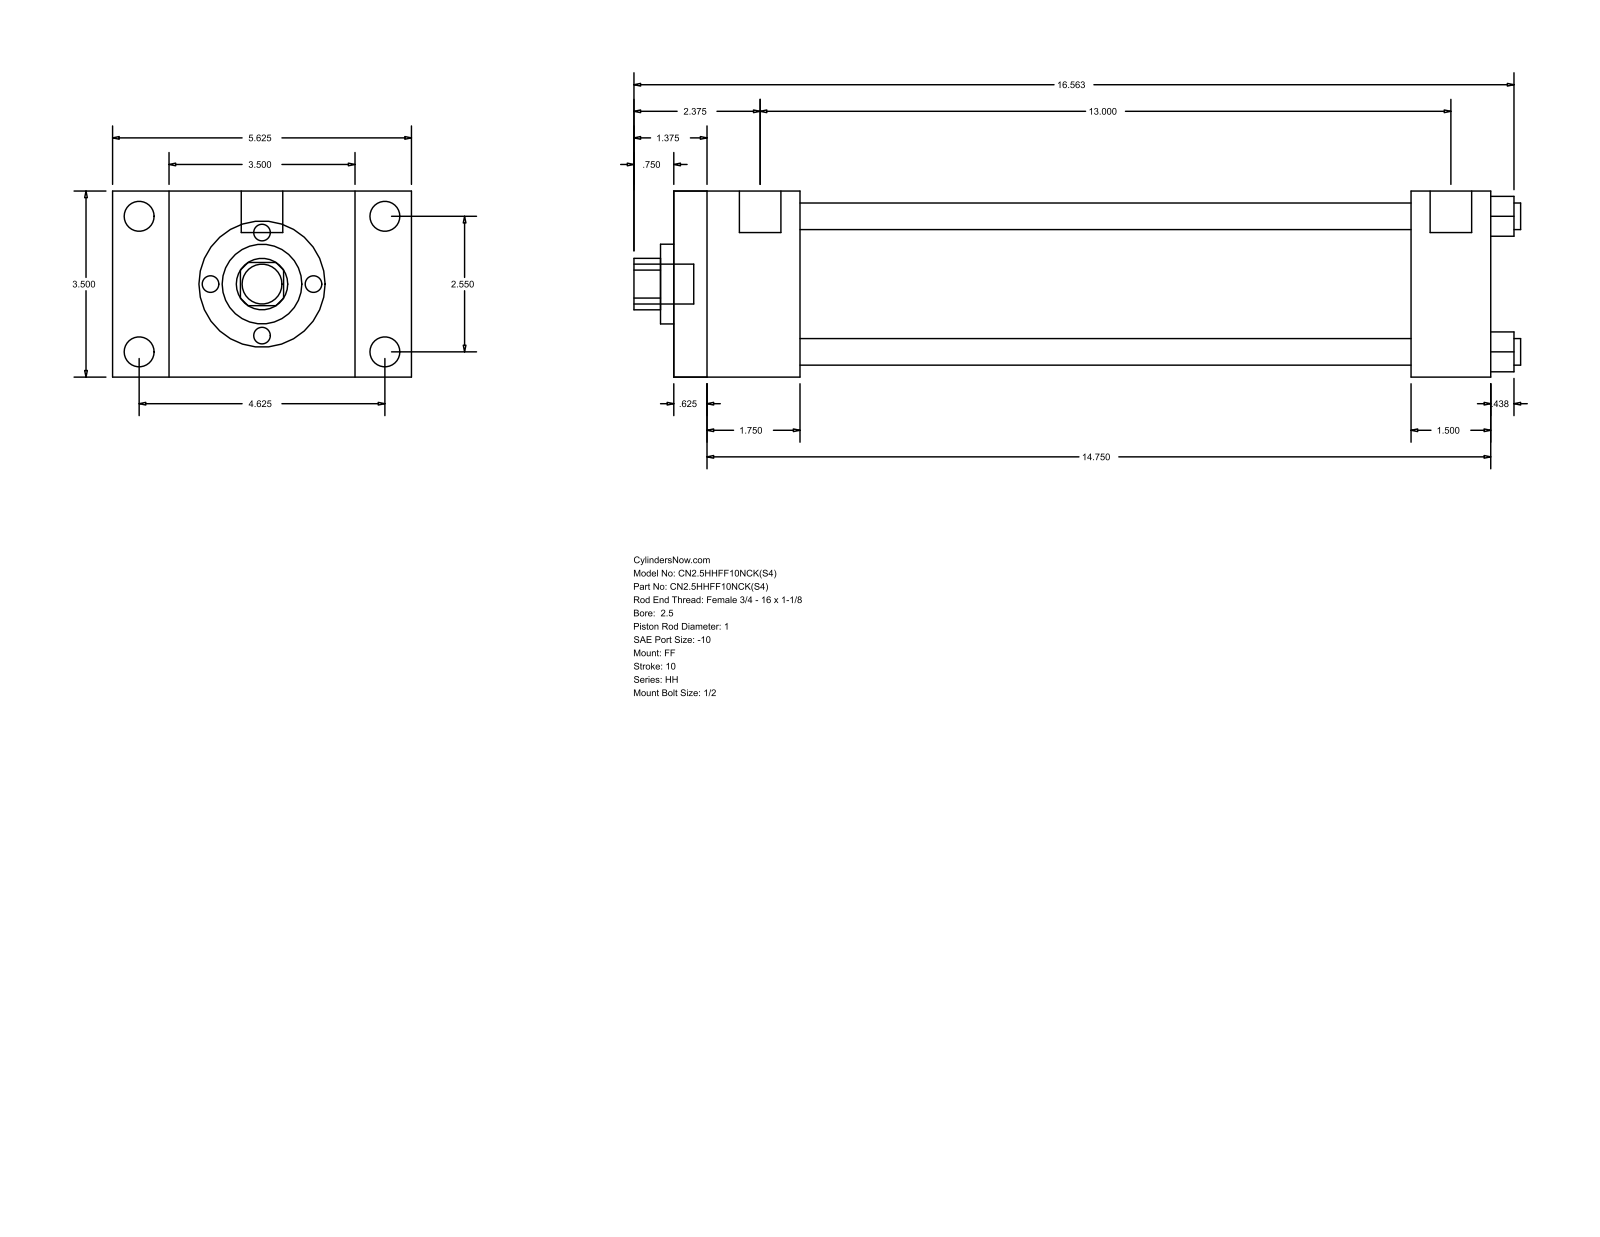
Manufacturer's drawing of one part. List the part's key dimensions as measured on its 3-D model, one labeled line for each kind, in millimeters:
Part name (STEP PRODUCT): HH_FF__0250_1
STEP written by: GSSL Pune (CONFIG_CONTROL_DESIGN)
Units: millimetres
Bodies: 0 solids, 92 faces (64 planar, 28 cylindrical, 0 other)
Overall size (bounding box): 423.86 × 142.88 × 88.9
Round holes (diameter × count): ⌀12.7 ×4, ⌀25.4 ×1, ⌀38.1 ×1, ⌀73.03 ×1
Round bosses / shafts (diameter × count): ⌀14.3 ×4, ⌀5.56 ×4, ⌀19.84 ×2, ⌀19.05 ×1
Partial cylindrical surfaces — rounded edges, fillets, slot ends (radius × count): R12.29 ×1
Main face-to-face distances: 88.9, 390.52, 15.87, 374.65, 60.33, 44.46, 330.19, 352.43, 336.56, 292.1
Hole centre spacings: 45.79, 64.76, 91.58
